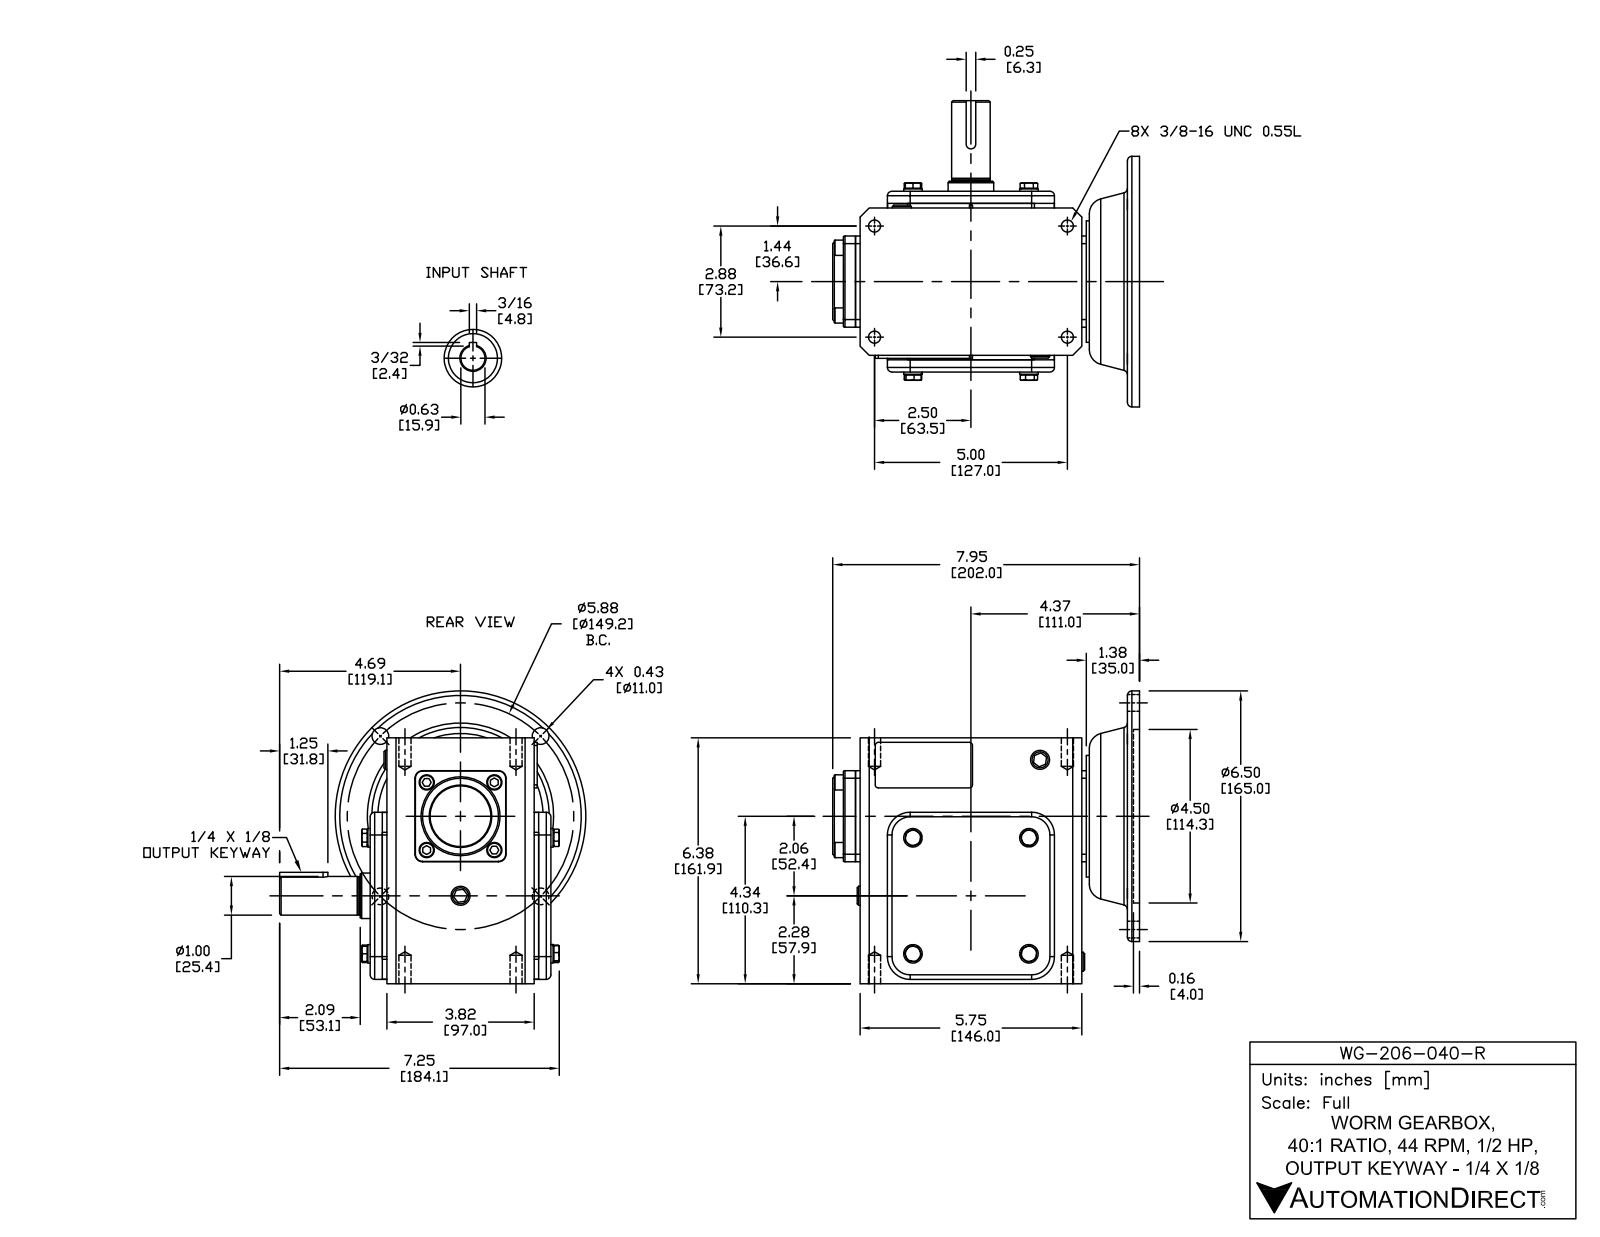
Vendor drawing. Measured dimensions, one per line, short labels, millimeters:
name: WG-206-040-R
written by: SolidWorks 2015 (CONFIG_CONTROL_DESIGN)
unit: mm
bodies: 43 solids, 610 faces (300 planar, 182 cylindrical, 128 other)
size: 202 × 201.6 × 192.8
volume: 2 815 000 mm³; area: 263 000 mm²
holes: 4× ⌀8, 4× ⌀10.3, 1× ⌀15, 1× ⌀15.9, 1× ⌀30, 1× ⌀37, 1× ⌀42, 1× ⌀90, 1× ⌀114.3
bosses: 8× ⌀10, 4× ⌀12.2, 1× ⌀165, 1× ⌀80, 1× ⌀52, 1× ⌀40, 1× ⌀30, 1× ⌀29
rounds: 8× R2, 8× R3, 4× R5, 4× R15, 2× R0.5, 2× R1, 1× R3.2, 1× R69
face distances: 8, 3, 103, 111, 11, 108, 100, 161.9, 119, 18
hole spacings: 74.6, 105.5, 52.8, 73.2, 117.6, 127, 146.6, 149.2
